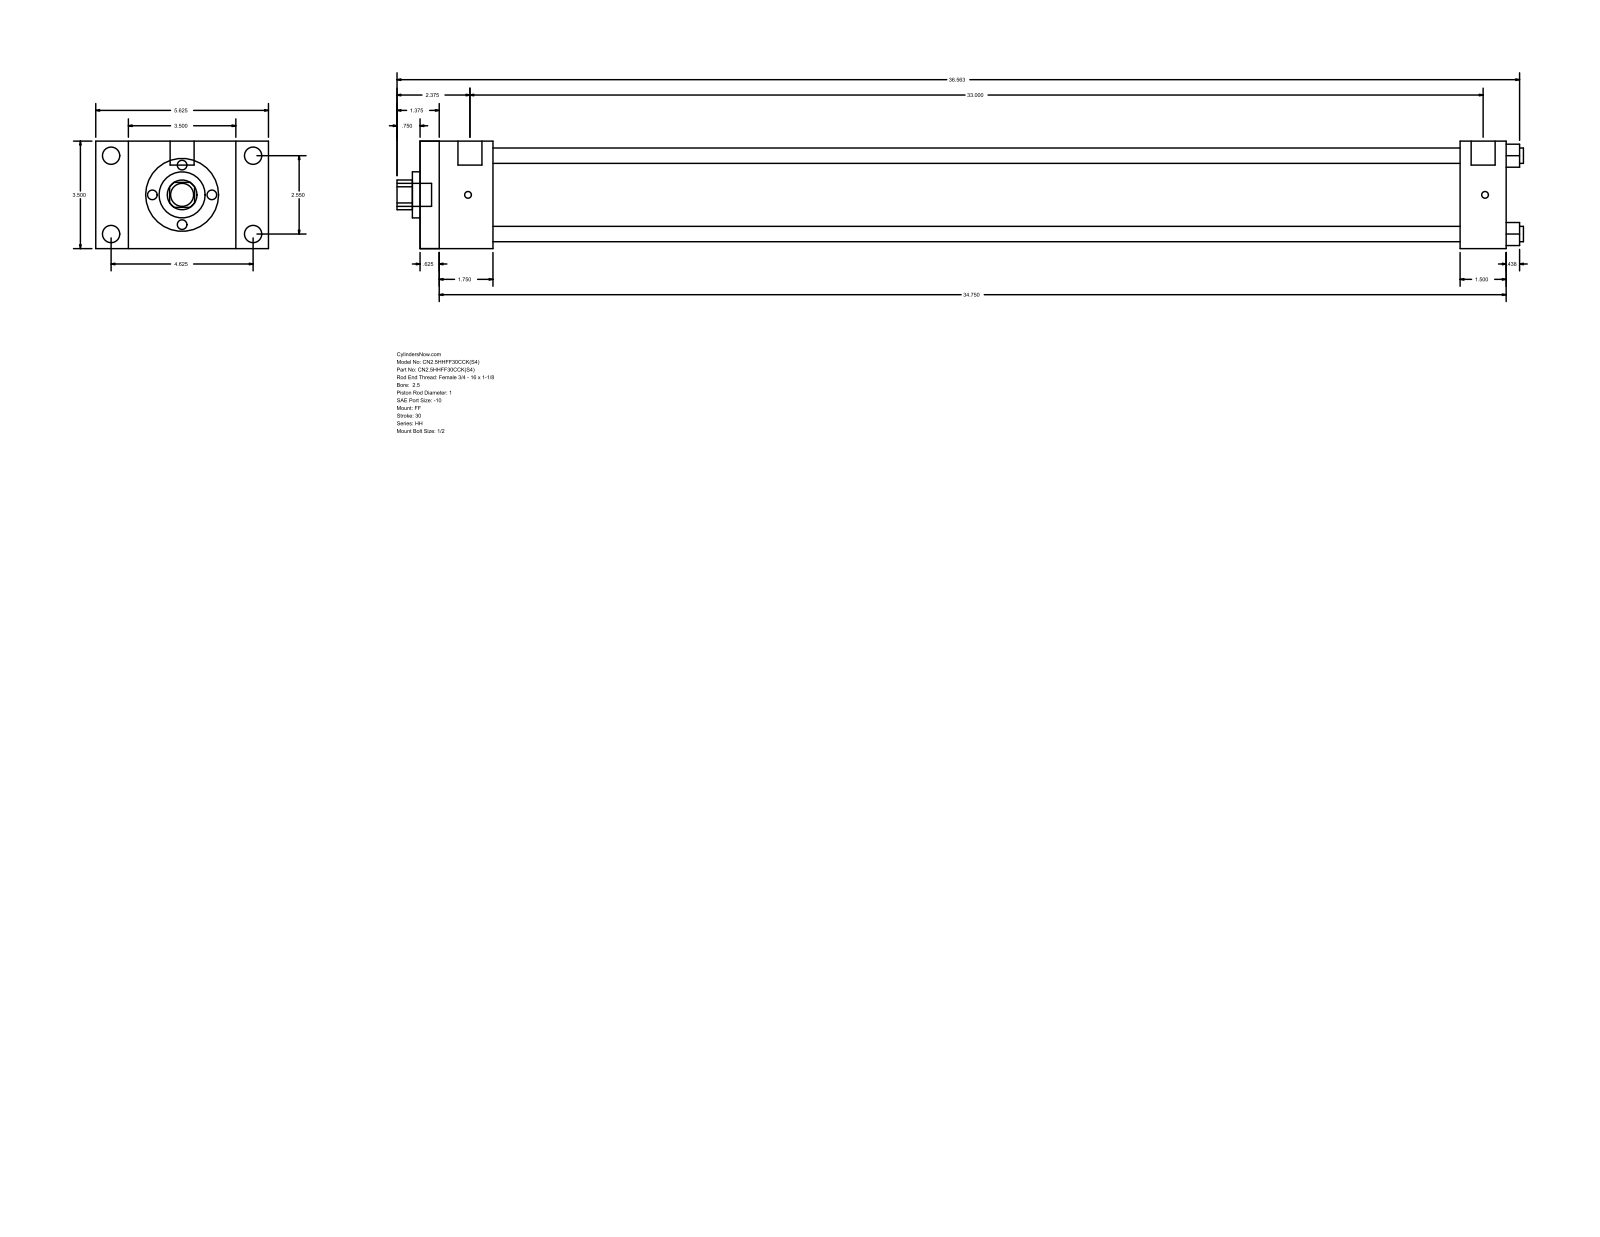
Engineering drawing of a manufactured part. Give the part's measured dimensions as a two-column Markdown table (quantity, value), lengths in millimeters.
| quantity | value |
| --- | --- |
| part name | HH_FF__0250_1 |
| STEP written by | GSSL Pune (CONFIG_CONTROL_DESIGN) |
| units | millimeters |
| bodies | 0 solids, 92 faces (64 planar, 28 cylindrical, 0 other) |
| overall size | 931.86 × 142.88 × 88.9 |
| round holes (diameter × count) | 12.7 × 4, 25.4 × 1, 38.1 × 1, 73.03 × 1 |
| round bosses / shafts (diameter × count) | 14.3 × 4, 5.56 × 4, 19.84 × 2, 19.05 × 1 |
| partial cylindrical surfaces (radius × count) | 12.29 × 1 |
| main face-to-face distances | 88.9, 898.53, 15.87, 882.66, 60.33, 44.46, 838.2, 860.43, 844.56, 800.1 |
| hole center spacings | 45.79, 64.76, 91.58 |
